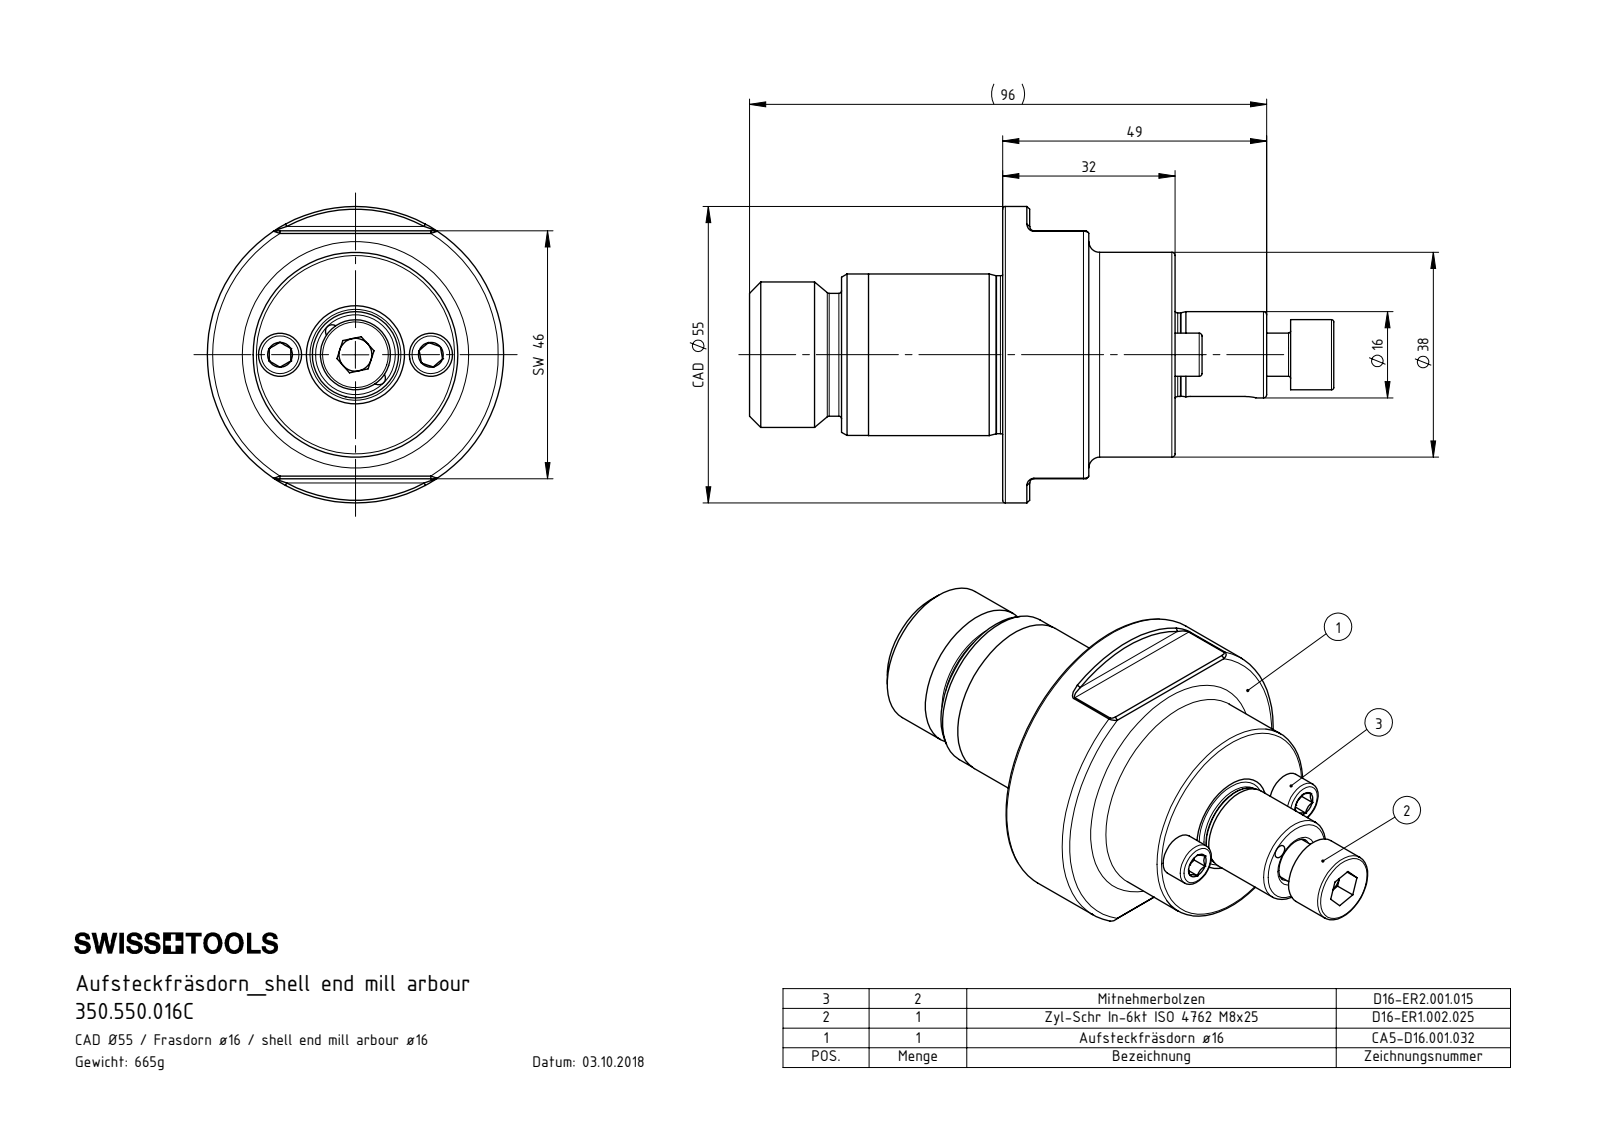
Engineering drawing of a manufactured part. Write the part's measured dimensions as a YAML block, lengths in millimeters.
part_name: "D16-ER1.002.025_A; D16-ER2.001.015_B; CA5-D16.001.032_B; 350.550.016C"
step_written_by: "SolidWorks 2022 (CONFIG_CONTROL_DESIGN)"
units: millimeters
bodies: {solids: 4, faces: 247, planar: 52, cylindrical: 72, other: 123}
overall_size: [108.45, 55, 55]
volume: 84748
surface_area: 19636
round_holes:
  - {diameter: 2.5, count: 3}
  - {diameter: 3.3, count: 2}
  - {diameter: 6, count: 2}
  - {diameter: 6.8, count: 1}
  - {diameter: 8.5, count: 1}
round_bosses_or_shafts:
  - {diameter: 8, count: 3}
  - {diameter: 4, count: 2}
  - {diameter: 3, count: 2}
  - {diameter: 55, count: 1}
  - {diameter: 38, count: 1}
  - {diameter: 30, count: 1}
  - {diameter: 29.95, count: 1}
  - {diameter: 29.3, count: 1}
partial_cylinders:
  - {radius: 0.8, count: 2}
  - {radius: 2, count: 2}
face_to_face_distances: [16, 32, 47, 63, 79, 46, 29.9, 61.9, 17.1, 45.9]
hole_center_spacings: [6.12, 10.6, 14, 18.83, 12.25, 28]
